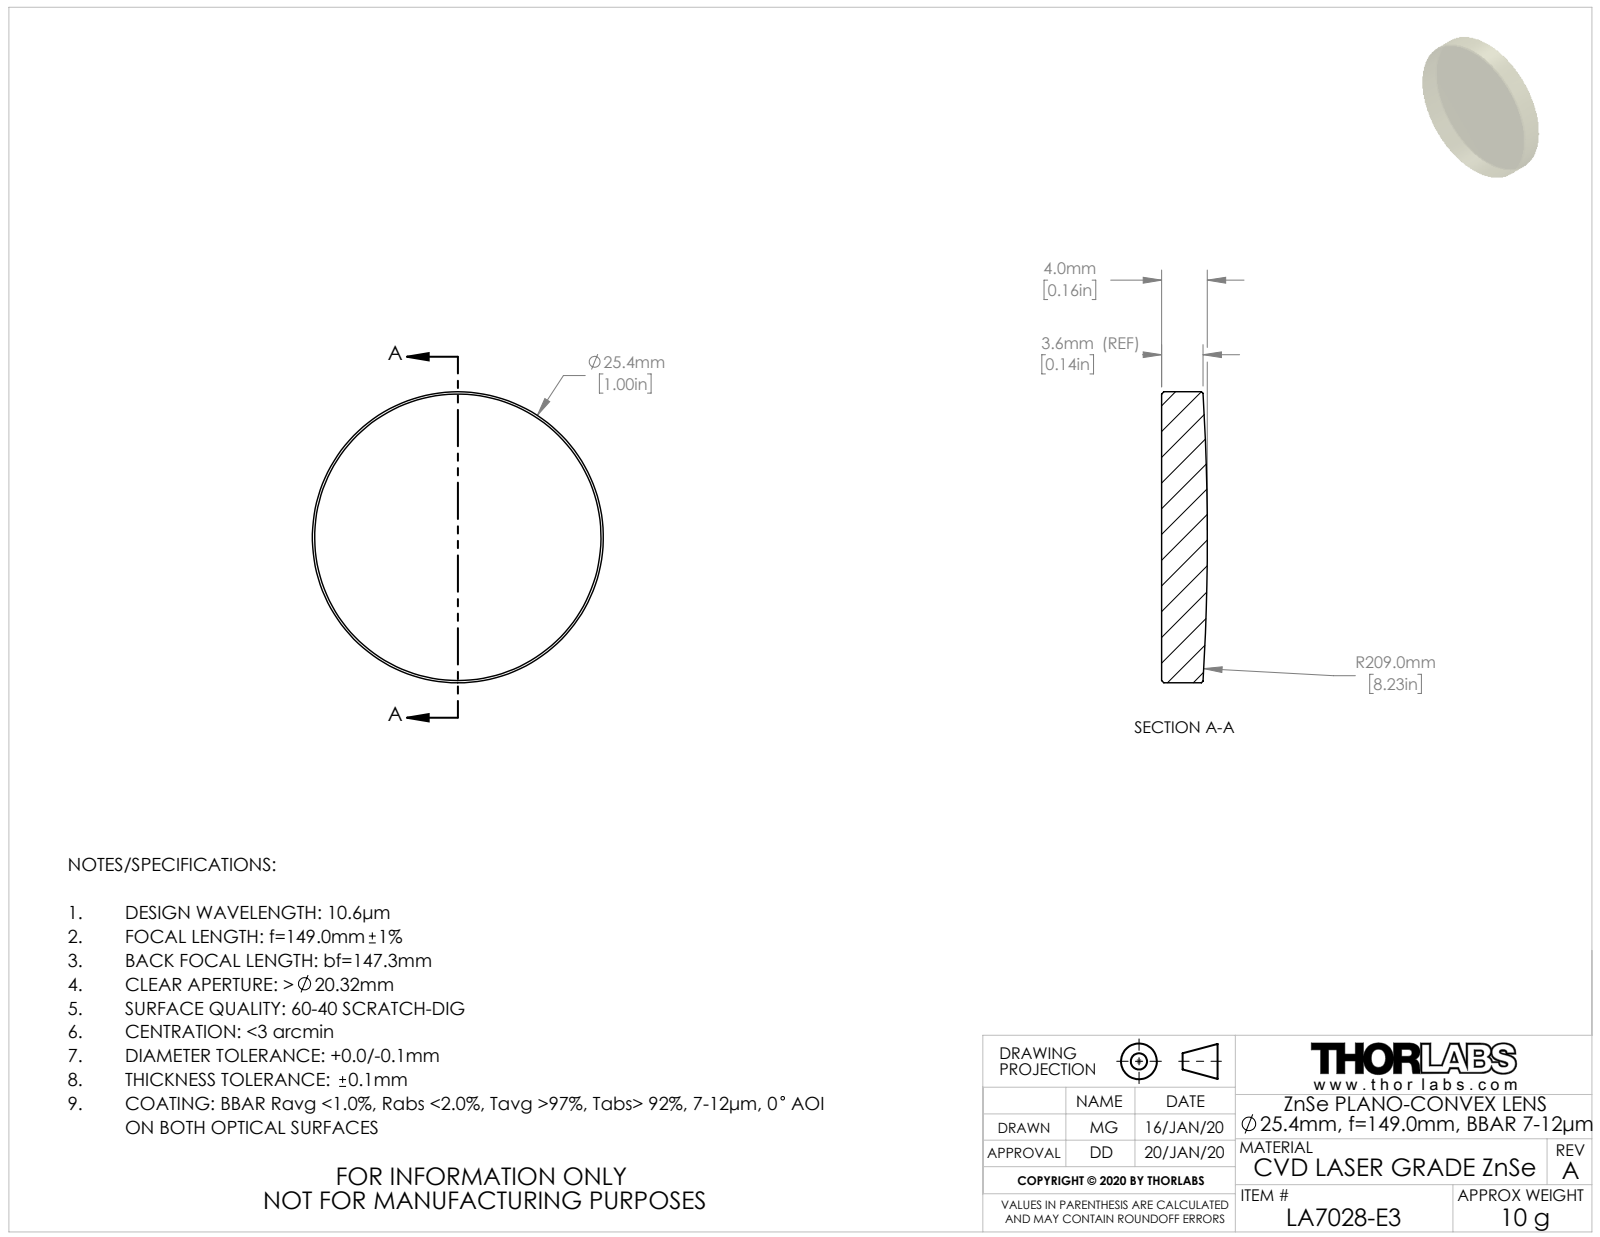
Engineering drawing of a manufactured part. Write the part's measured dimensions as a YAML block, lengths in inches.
part_name: "TTN206027-E0W"
step_written_by: "SolidWorks 2018 (CONFIG_CONTROL_DESIGN)"
units: inches
bodies: {solids: 1, faces: 9, planar: 1, cylindrical: 2, other: 6}
overall_size: [1, 1, 0.157]
volume: 0.118
surface_area: 1.995
round_bosses_or_shafts:
  - {diameter: 1, count: 1}
